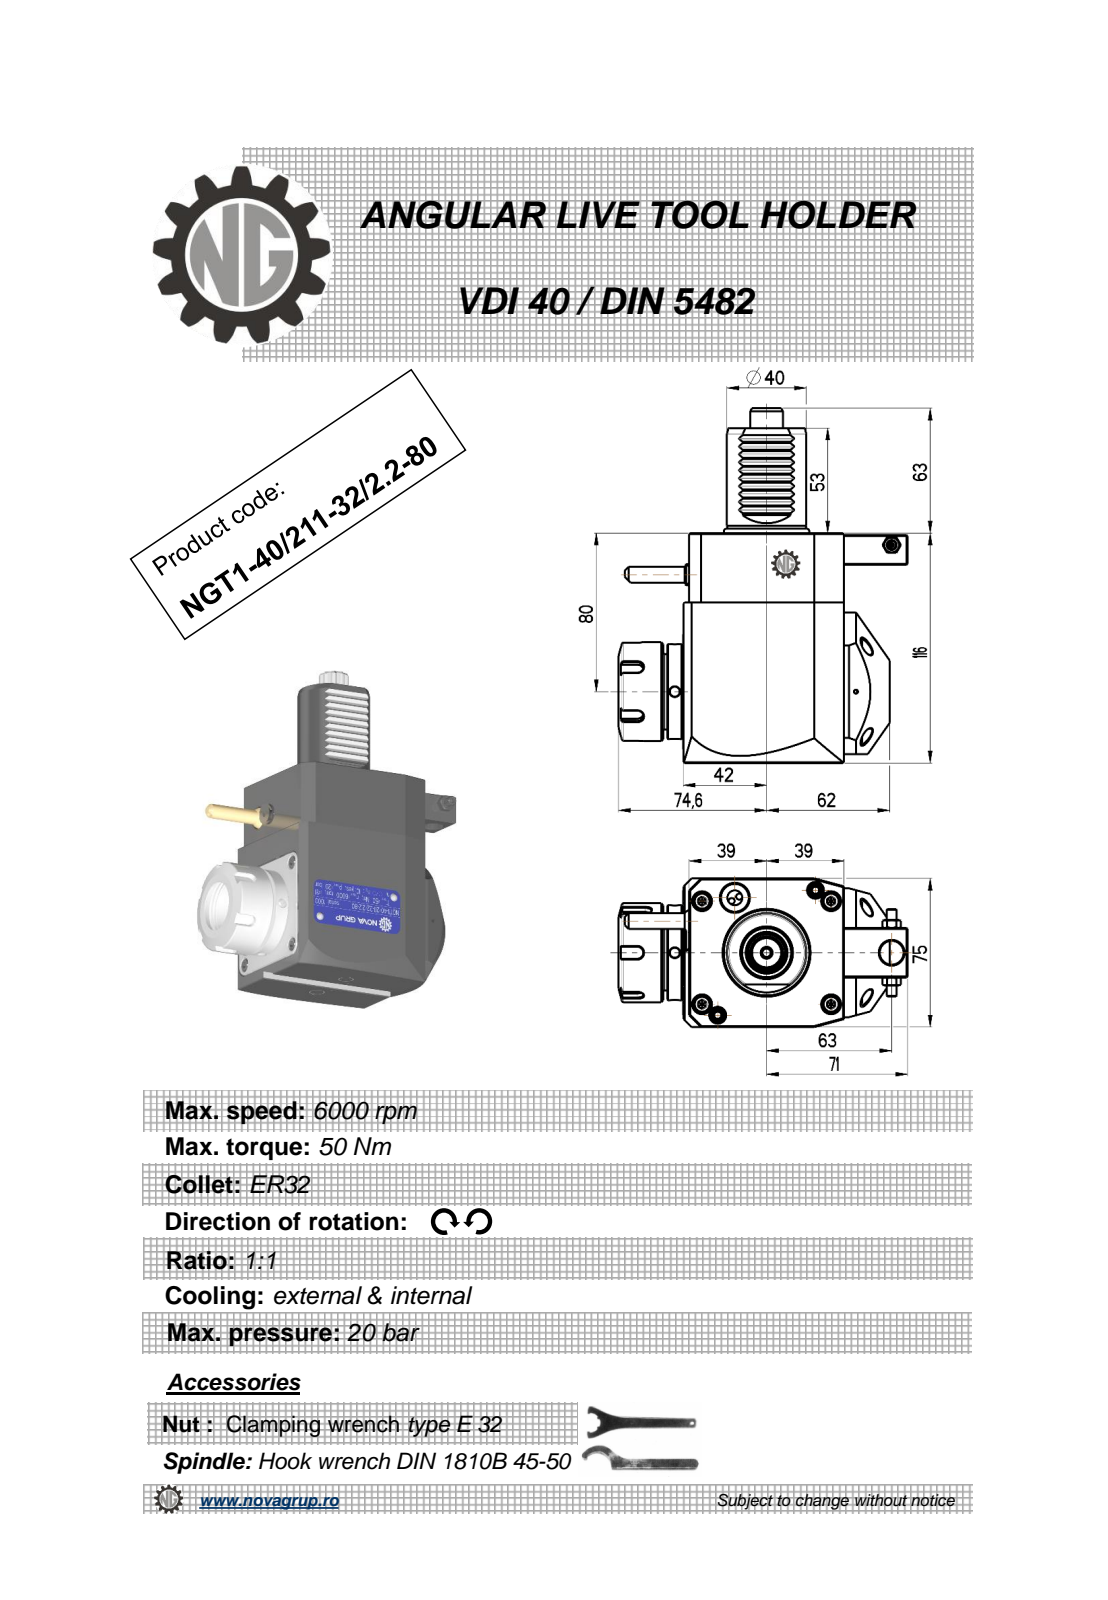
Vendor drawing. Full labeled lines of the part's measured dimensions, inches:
Part name (STEP PRODUCT): NGT1_40_211_32_2_2_80
STEP written by: PRO/ENGINEER BY PARAMETRIC TECHNOLOGY CORPORATION, 2010280 (CONFIG_CONTROL_DESIGN)
Units: inches
Bodies: 1 solid, 451 faces (183 planar, 124 cylindrical, 144 other)
Overall size (bounding box): 7.047 × 5.732 × 3.016
Volume: 53.76 in³ · Surface area: 108.6 in²
Round holes (diameter × count): ⌀0.197 ×3, ⌀0.165 ×2, ⌀0.118 ×1, ⌀0.374 ×1, ⌀0.472 ×1, ⌀1.063 ×1
Round bosses / shafts (diameter × count): ⌀1.969 ×1, ⌀1.89 ×1, ⌀1.614 ×1, ⌀1.575 ×1, ⌀0.441 ×1, ⌀0.353 ×1, ⌀0.315 ×1, ⌀0.197 ×1
Partial cylindrical surfaces — rounded edges, fillets, slot ends (radius × count): R0.119 ×18, R0.01 ×12, R0.012 ×10, R0.009 ×6, R0.118 ×5, R0.02 ×1, R0.266 ×1, R0.324 ×1
Main face-to-face distances: 2.953, 4.567, 3.189, 0.118, 3.071, 0.11, 3.181, 4.409, 0.984, 0.295
Hole centre spacings: 0.824, 1.821, 2.407, 2.48, 2.854, 4.301, 5.195
